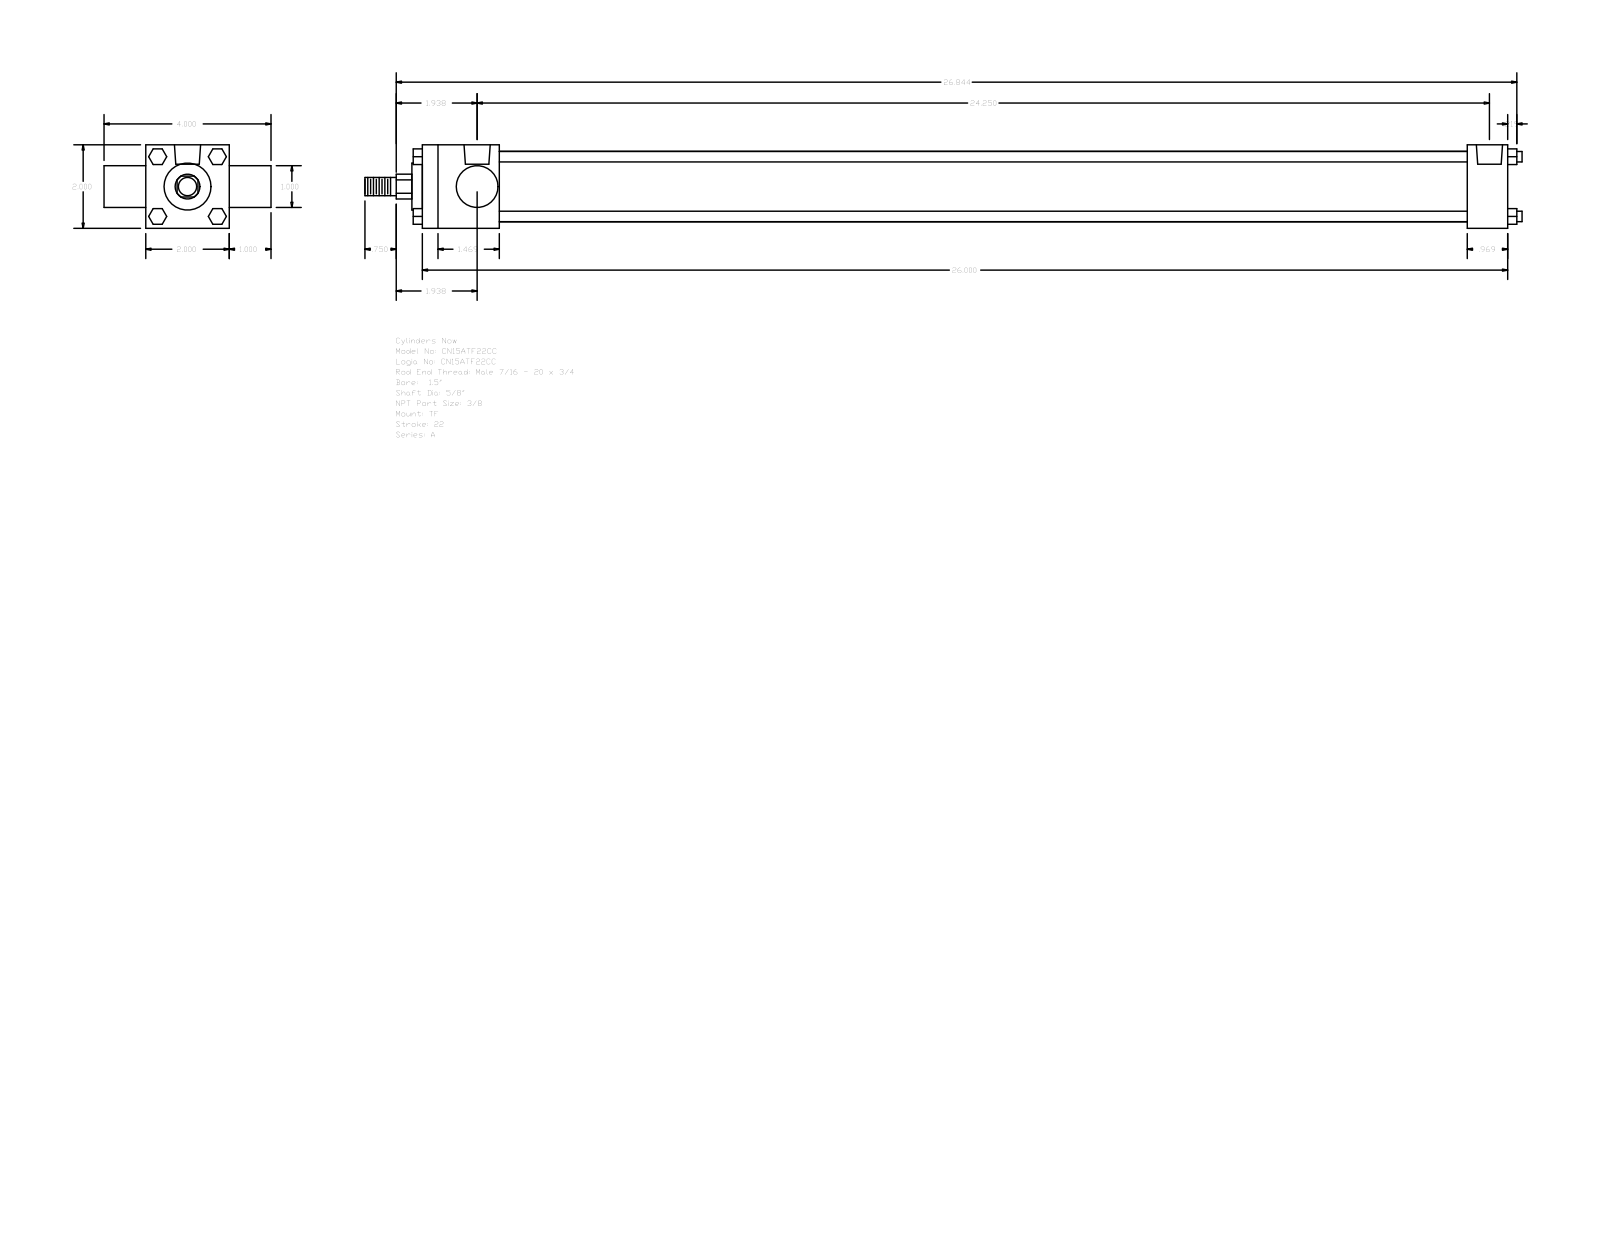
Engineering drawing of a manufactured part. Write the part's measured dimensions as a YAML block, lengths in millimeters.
part_name: "A_TF__0150_0.625"
step_written_by: "GSSL Pune (CONFIG_CONTROL_DESIGN)"
units: millimeters
bodies: {solids: 0, faces: 120, planar: 92, cylindrical: 28, other: 0}
overall_size: [704.06, 101.6, 50.8]
round_holes:
  - {diameter: 5.56, count: 3}
  - {diameter: 15.93, count: 2}
round_bosses_or_shafts:
  - {diameter: 6.35, count: 4}
  - {diameter: 42.93, count: 1}
  - {diameter: 28.57, count: 1}
  - {diameter: 25.4, count: 1}
  - {diameter: 15.88, count: 1}
  - {diameter: 11.11, count: 1}
partial_cylinders:
  - {radius: 7.54, count: 1}
face_to_face_distances: [50.8, 660.39, 25.4, 76.2, 46.83, 635.79, 588.96, 613.56, 24.6, 101.6]
hole_center_spacings: [3.97, 611.98, 608.01, 615.95]
